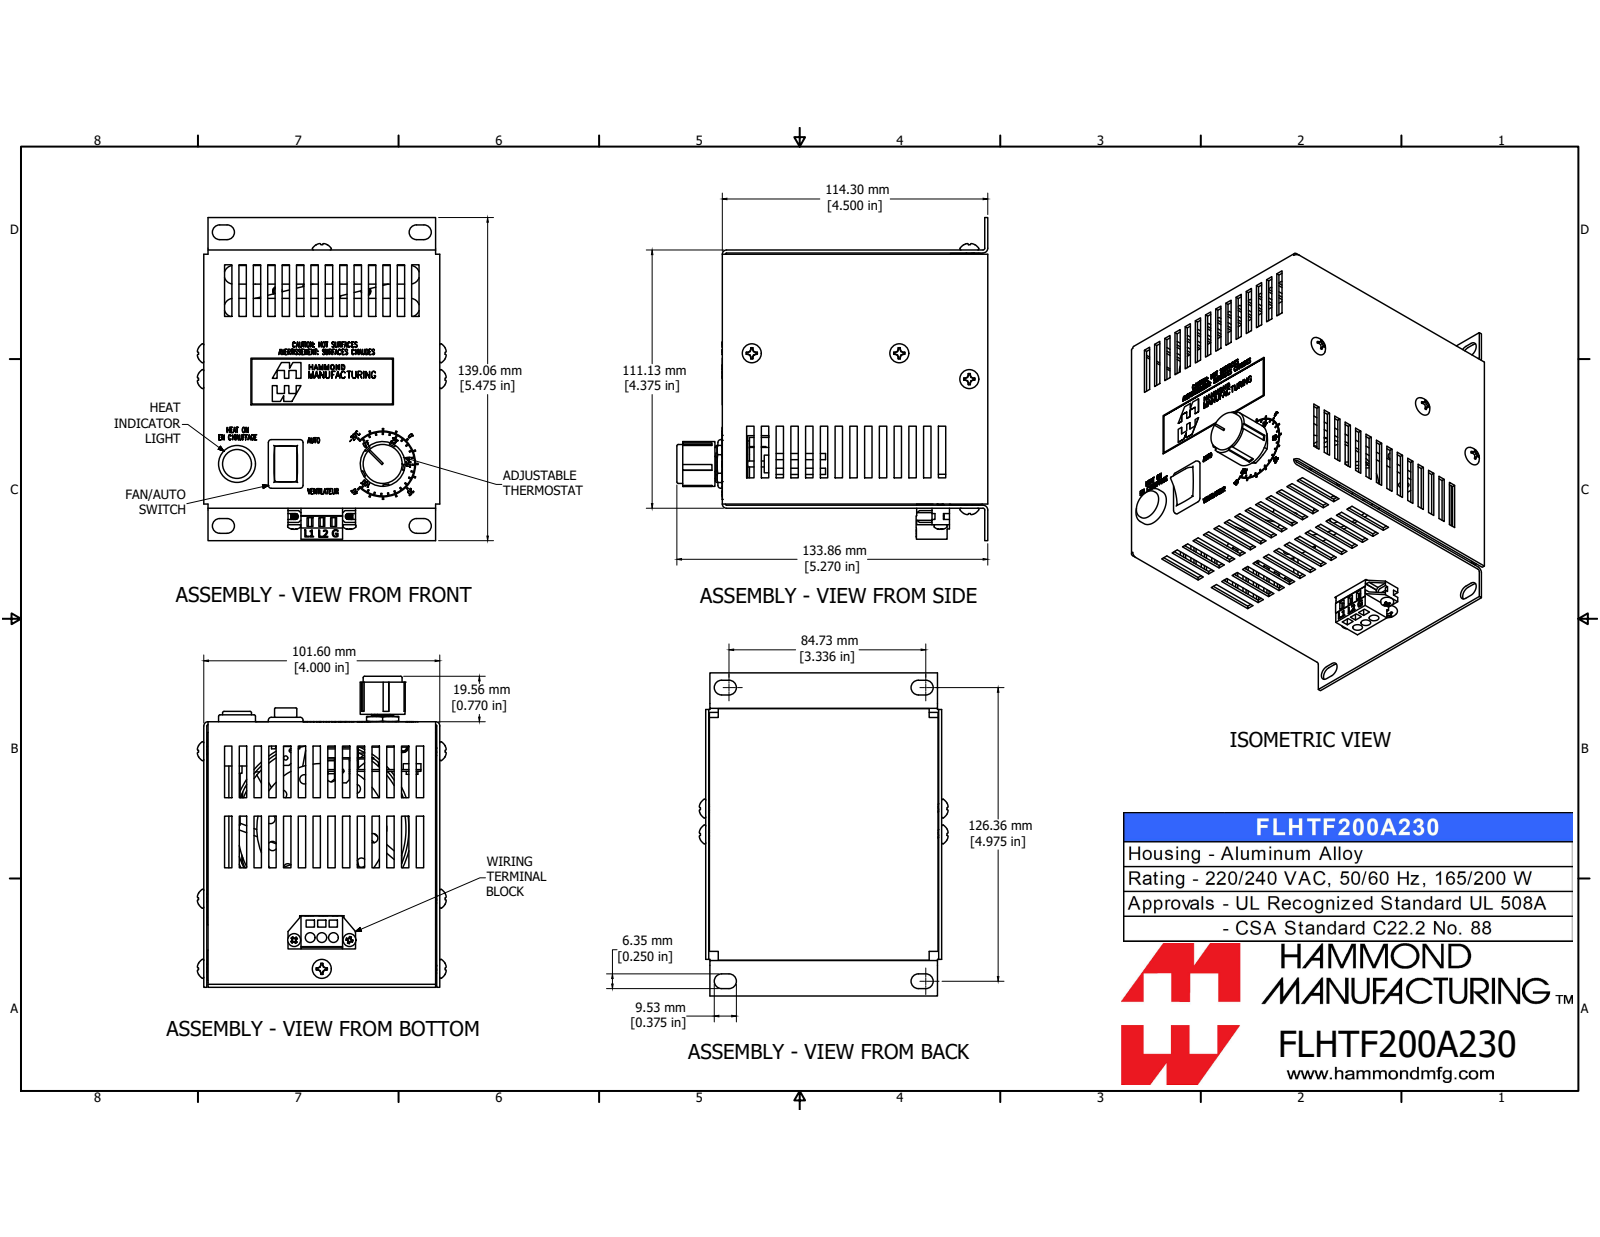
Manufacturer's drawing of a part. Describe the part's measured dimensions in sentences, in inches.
The part is named "FLHTF200A230". Its 3-D file was written by "SolidWorks 2019 (AUTOMOTIVE_DESIGN)". It is 17 solids with 4154 faces: 3643 planar, 274 cylindrical and 237 other. Overall it measures 5.475 by 5.27 by 4.218 inches. Its volume is 8.774 cubic inches and its surface area 274 square inches. Round holes: 4 of diameter 0.137, 4 of diameter 0.182, 4 of diameter 0.203, 3 of diameter 0.165, 2 of diameter 0.085, 2 of diameter 0.12, 2 of diameter 0.13, 2 of diameter 0.189, 1 of diameter 0.066, 1 of diameter 0.07, 1 of diameter 0.25, 1 of diameter 0.383. Round bosses or shafts: 4 of diameter 0.164, 4 of diameter 0.104, 2 of diameter 0.17, 2 of diameter 0.105, 1 of diameter 0.76, 1 of diameter 0.66, 1 of diameter 0.65, 1 of diameter 0.625. Partial cylindrical surfaces (rounded edges, fillets, slot ends): 38 of radius 0.125, 17 of radius 0.05, 12 of radius 0.025, 12 of radius 0.629, 9 of radius 0.15, 4 of radius 0.02, 4 of radius 0.071, 2 of radius 0.015. The main face-to-face distances are 0.051, 3.949, 0.1, 0.051, 4.324, 4, 3.898, 4.494, 4.394, 4.443. The hole center spacings are 2.756, 0.197, 0.275, 0.471, 0.531, 0.564, 0.565, 0.667.
